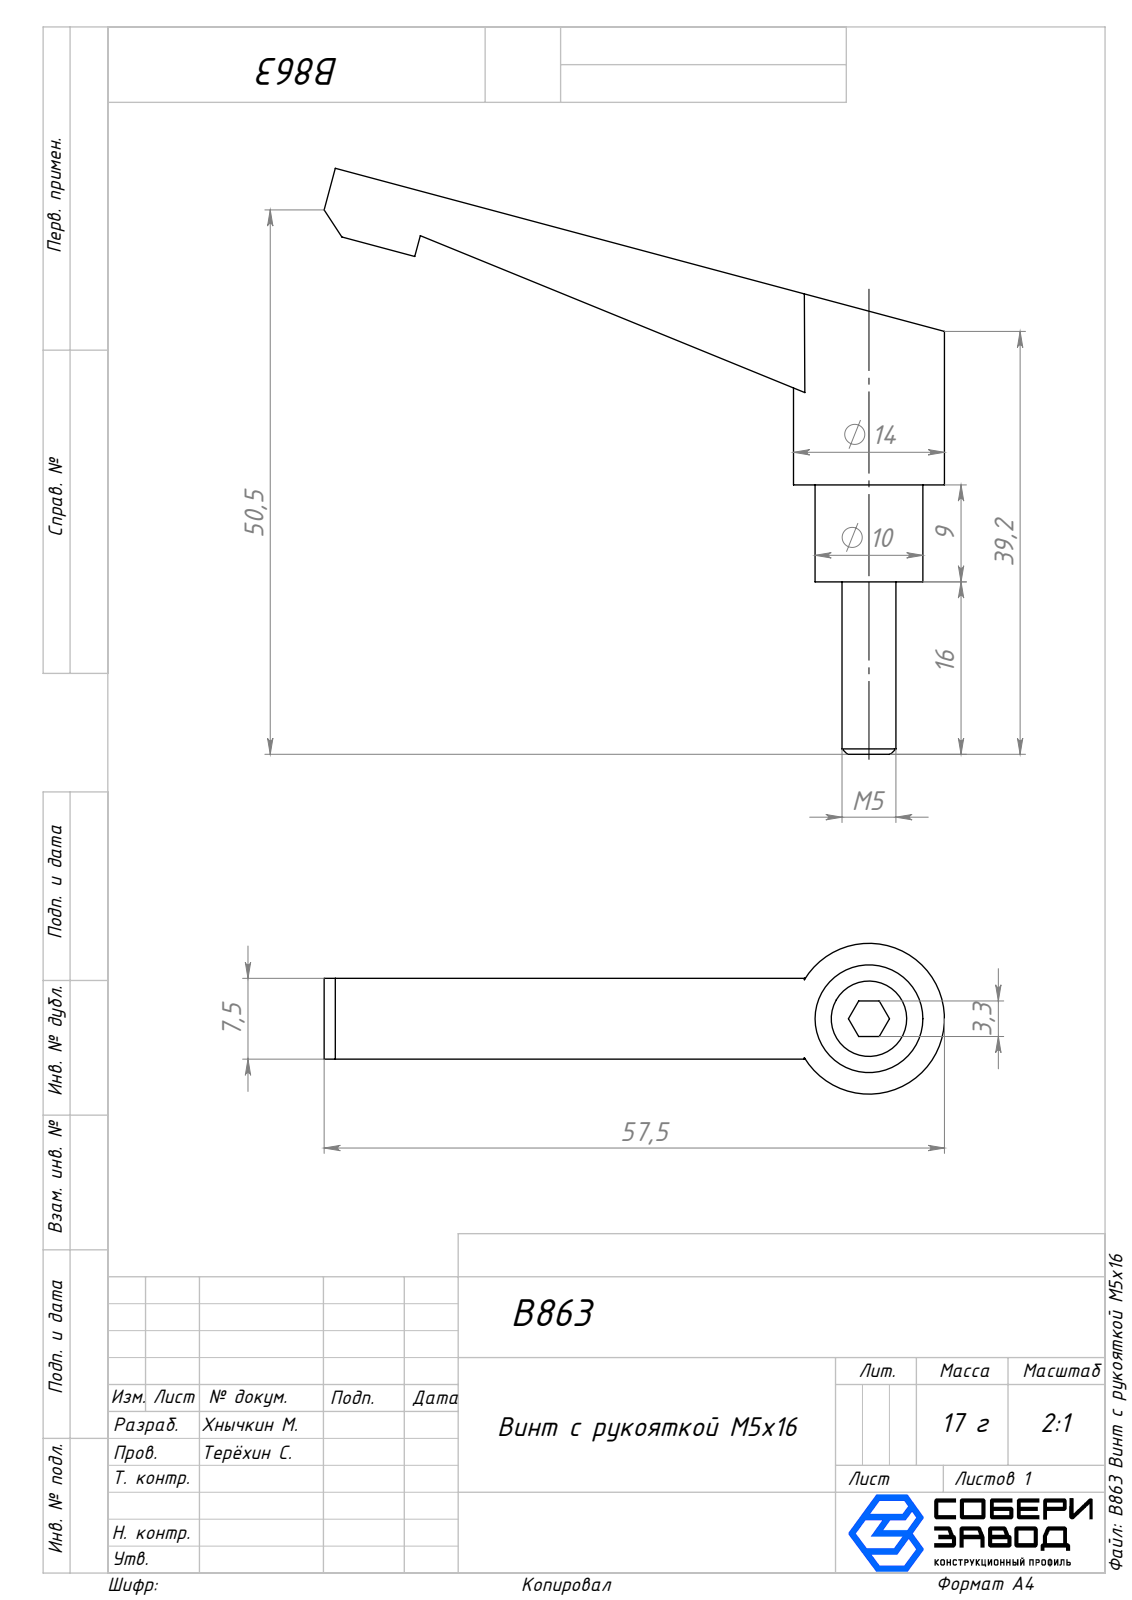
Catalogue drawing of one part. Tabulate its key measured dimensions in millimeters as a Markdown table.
| quantity | value |
| --- | --- |
| part name | Рукоятка_00; B863 Винт с рукояткой М5х16; Винтик_00; Винт с рукояткой_00 |
| STEP written by | SolidWorks 2025 (AUTOMOTIVE_DESIGN) |
| units | millimeters |
| bodies | 3 solids, 52 faces (32 planar, 18 cylindrical, 2 other) |
| overall size | 57.54 × 54.39 × 14 |
| volume | 4 610 mm³ |
| surface area | 4 369 mm² |
| round holes (diameter × count) | 3 × 1, 6 × 1, 10 × 1 |
| round bosses / shafts (diameter × count) | 14 × 1, 7 × 1, 5 × 1 |
| main face-to-face distances | 1, 7.5, 6.5, 5.5, 3.5, 10, 11, 9, 19, 20 |
